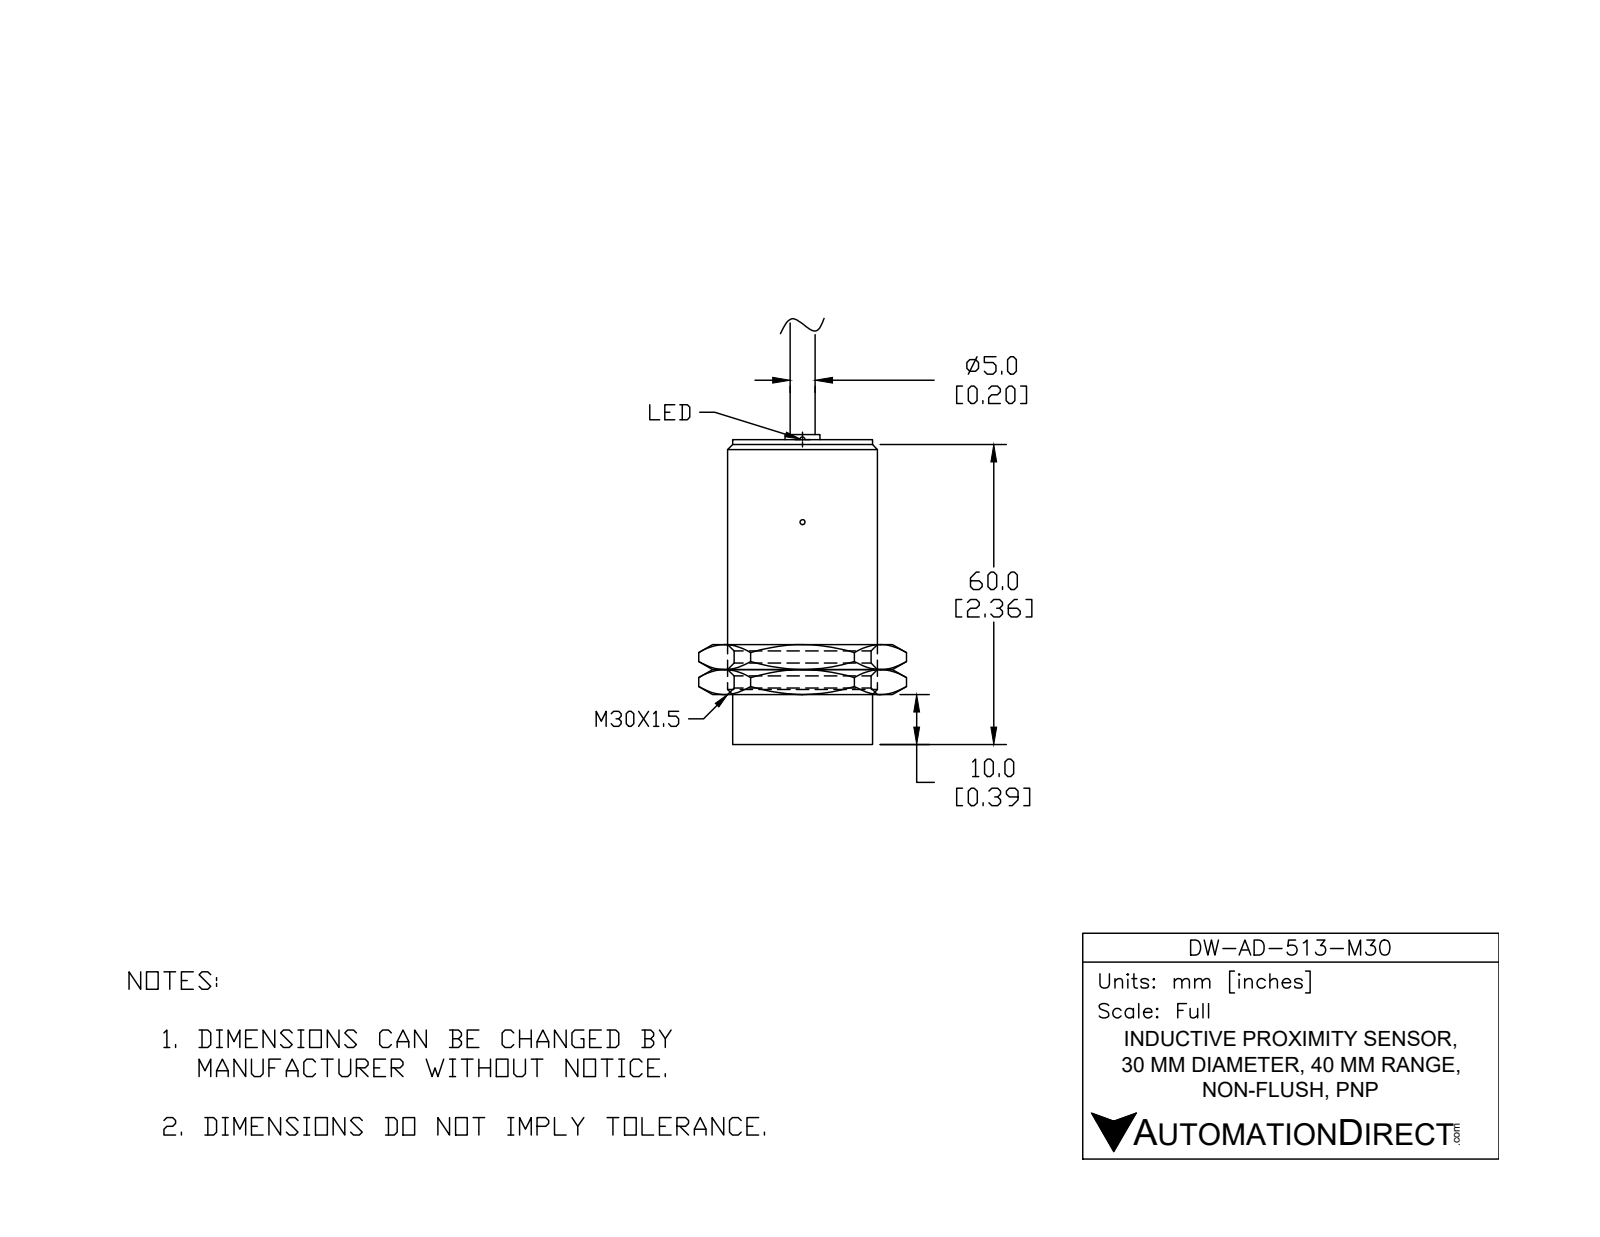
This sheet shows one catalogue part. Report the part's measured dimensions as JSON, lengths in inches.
{"part_name": "DW-AD-513-M30", "step_written_by": "SolidWorks 2017 (AUTOMOTIVE_DESIGN)", "units": "inches", "bodies": {"solids": 2, "faces": 16, "planar": 6, "cylindrical": 4, "other": 6}, "overall_size": [3.465, 1.181, 1.181], "volume_in3": 2.596, "surface_area_in2": 13.34, "round_bosses_or_shafts": [[1.181, 1], [1.083, 1], [0.413, 1], [0.197, 1]], "face_to_face_distances": [0.394, 2.402, 2.008, 2.431, 2.038, 0.03, 3.465, 3.071, 1.063, 1.033]}
